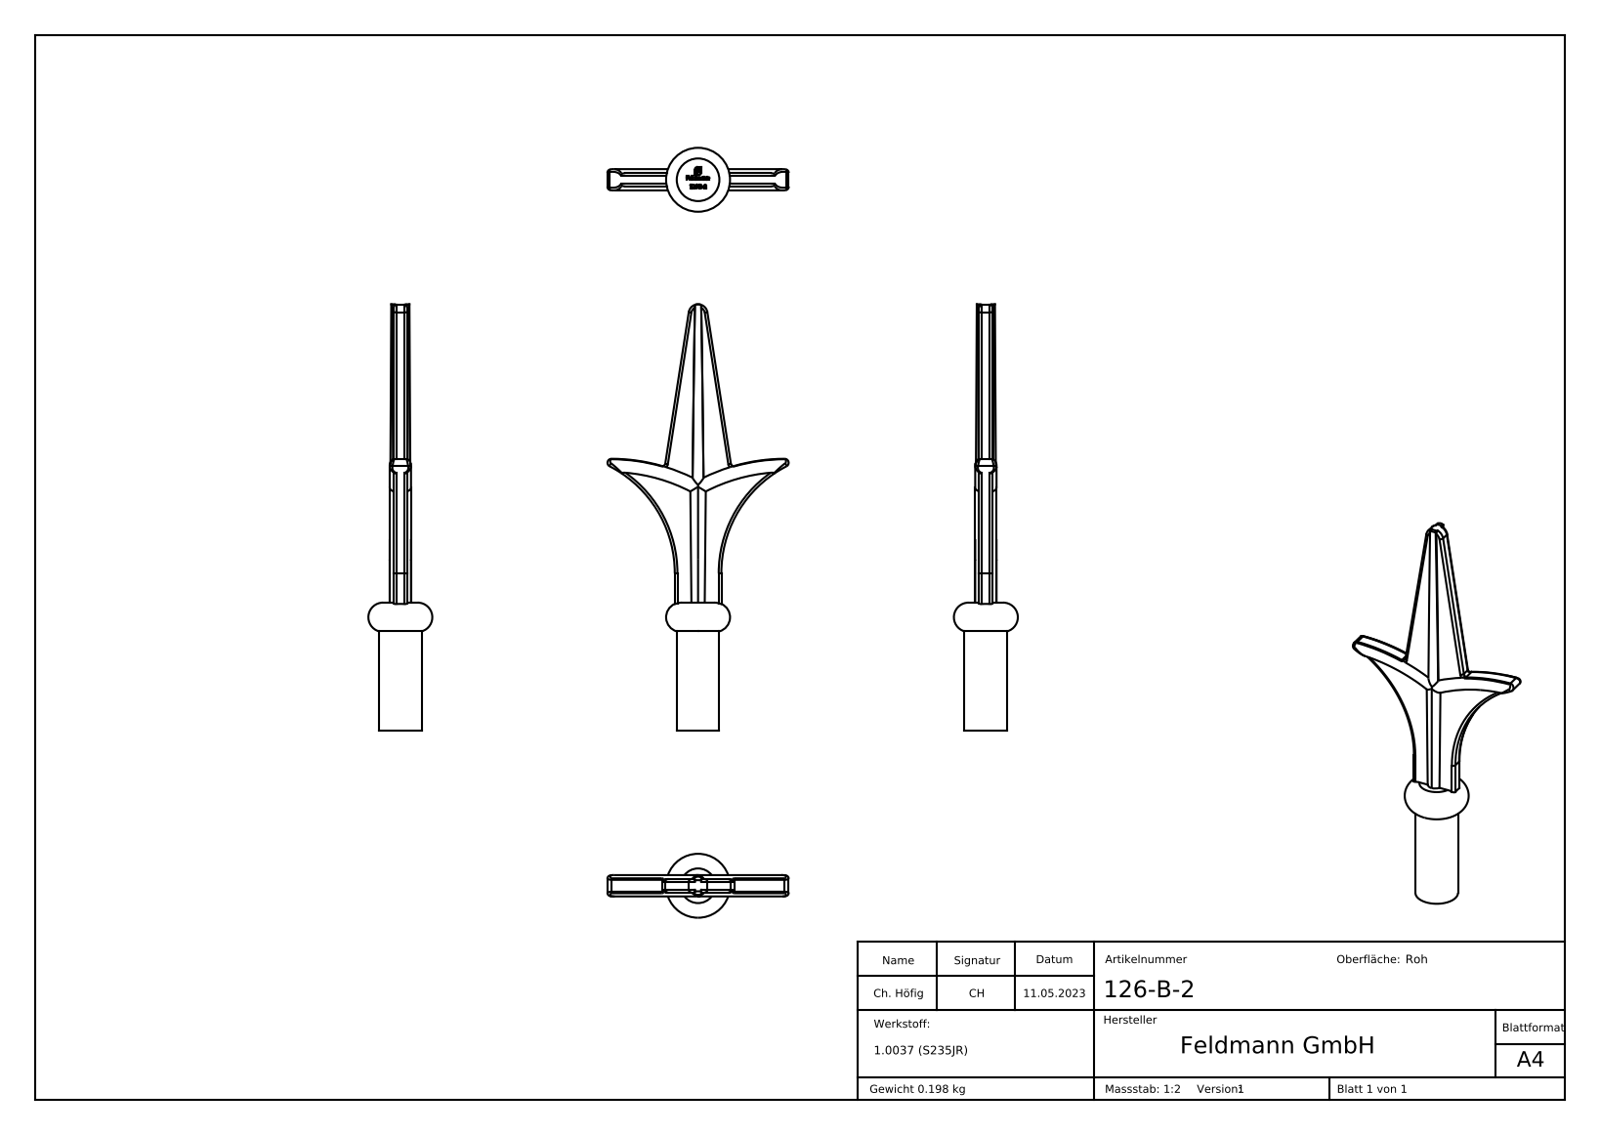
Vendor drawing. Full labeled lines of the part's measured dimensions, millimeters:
Part name (STEP PRODUCT): 126-B-2
STEP written by: SolidWorks 2018 (CONFIG_CONTROL_DESIGN)
Units: millimetres
Bodies: 1 solid, 312 faces (151 planar, 18 cylindrical, 143 other)
Overall size (bounding box): 160 × 68 × 24
Volume: 25 428 mm³ · Surface area: 9 784 mm²
Round bosses / shafts (diameter × count): ⌀16 ×1
Partial cylindrical surfaces — rounded edges, fillets, slot ends (radius × count): R1 ×10, R1.5 ×2, R45 ×2, R70 ×2, R3.54 ×1
Main face-to-face distances: 5, 48, 17.5, 47.9, 1.7, 0.34, 3.66, 0.44, 1.82, 1.69
